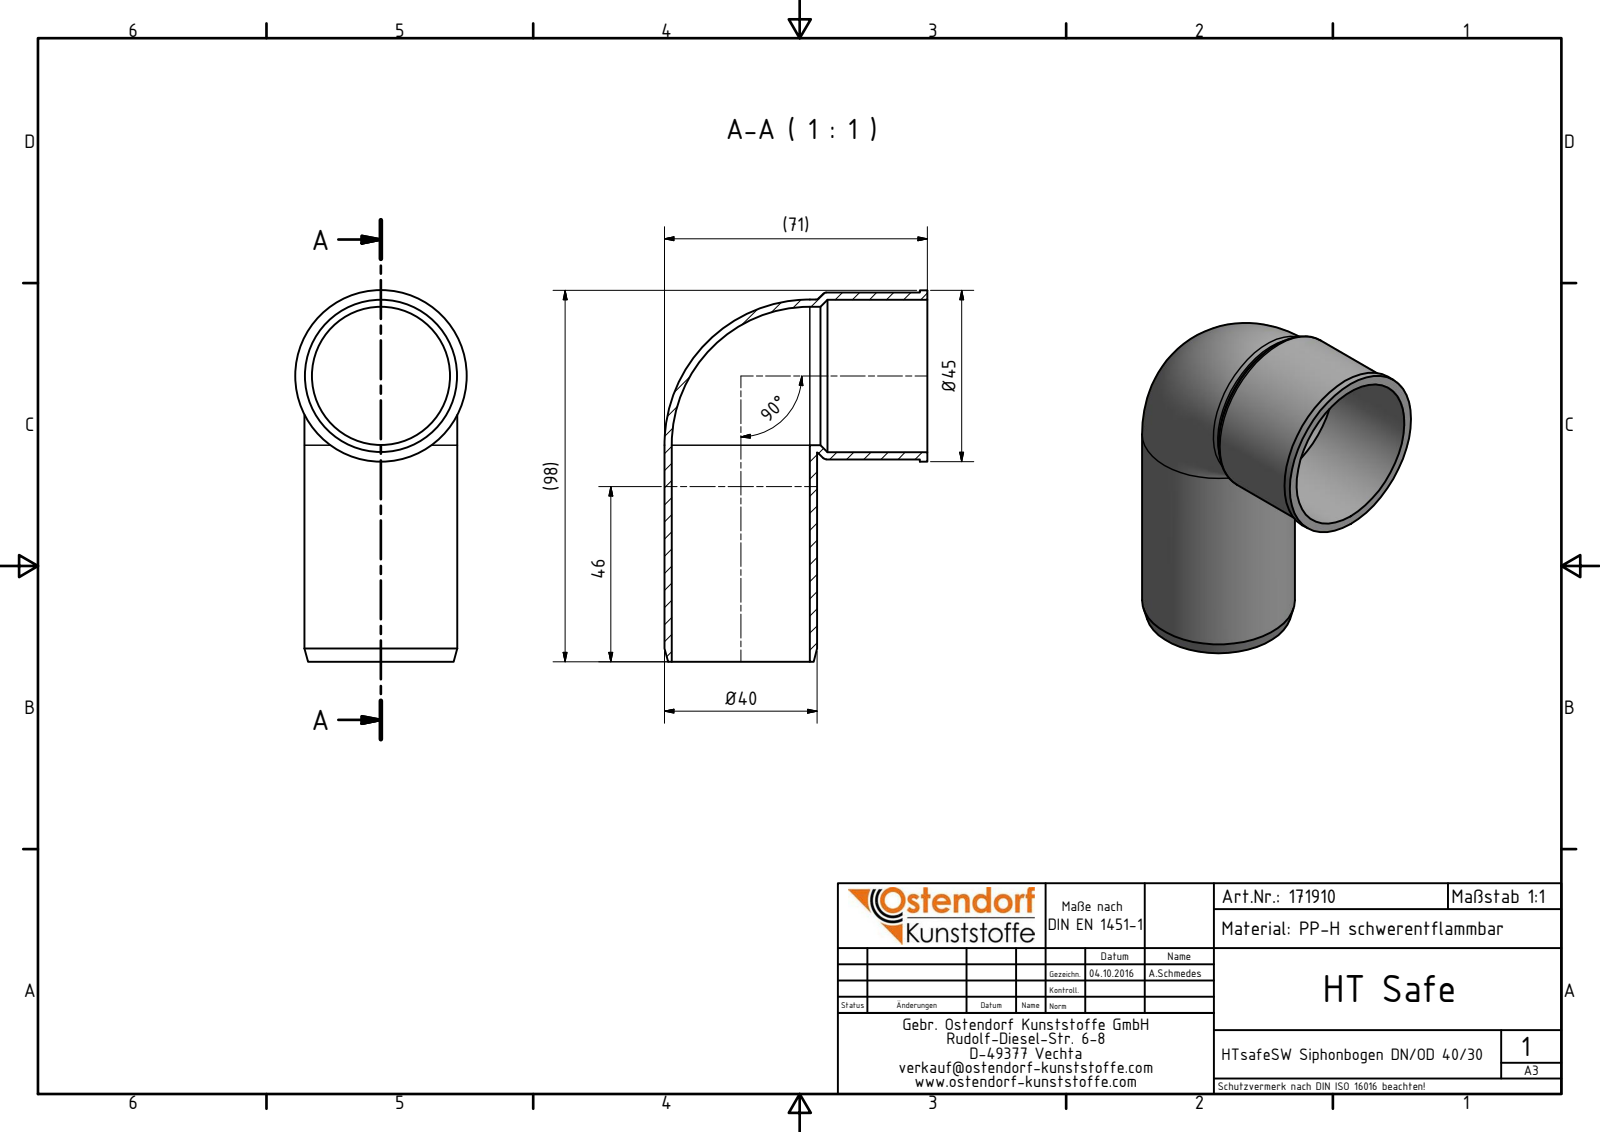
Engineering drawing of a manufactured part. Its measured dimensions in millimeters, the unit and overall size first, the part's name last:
Units: millimetres
Overall size (bounding box): 97.5 × 69.05 × 45
Round holes (diameter × count): ⌀36.3 ×2, ⌀40 ×1
Round bosses / shafts (diameter × count): ⌀40.1 ×2, ⌀45 ×1, ⌀43.8 ×1
Main face-to-face distances: 2
Volume: 26 778 mm³ · Surface area: 29 262 mm²
Bodies: 1 solid, 17 faces (3 planar, 7 cylindrical, 7 other)
Part name (STEP PRODUCT): 171910 HTsafeSW DN_OD 40_30
STEP written by: Autodesk Inventor 2016 (AUTOMOTIVE_DESIGN)
